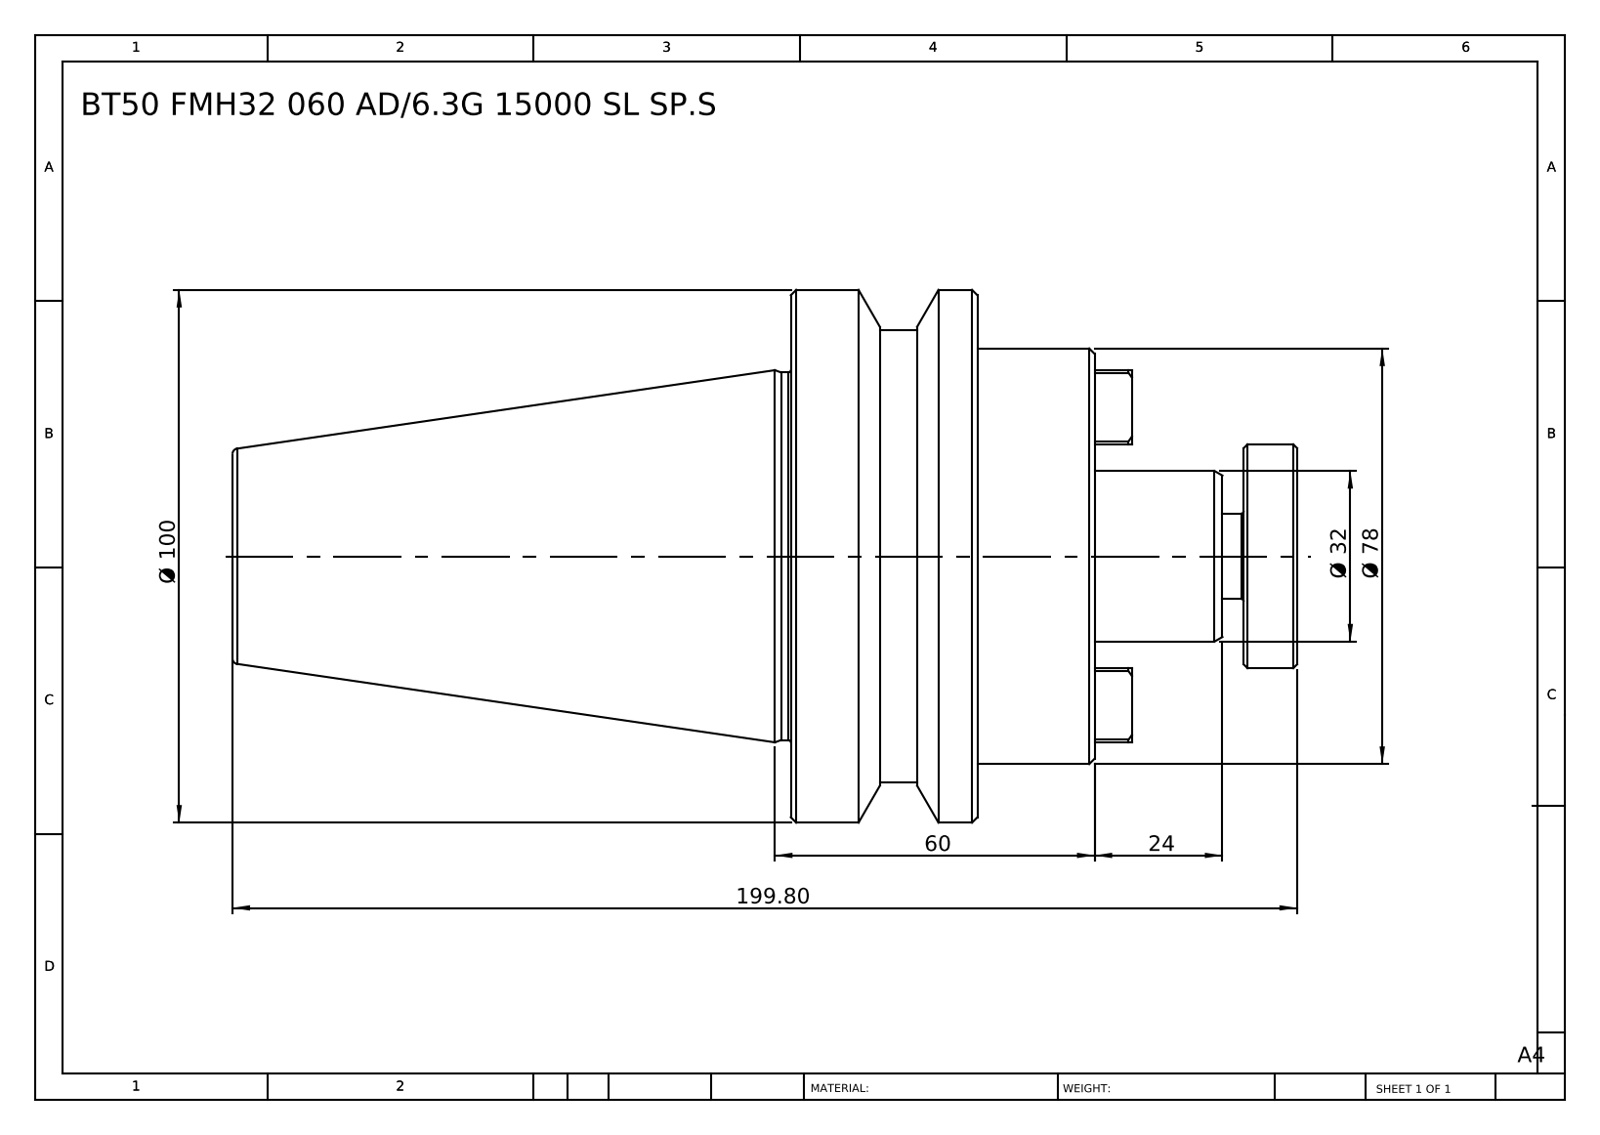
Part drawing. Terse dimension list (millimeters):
name: BT50 FMH32 060 AD-6.3G 15000 SL SP.S
written by: SolidWorks 2014 (CONFIG_CONTROL_DESIGN)
unit: mm
bodies: 1 solid, 77 faces (35 planar, 16 cylindrical, 26 other)
size: 199.8 × 100 × 100
volume: 651 665 mm³; area: 56 488 mm²
bosses: 1× ⌀100, 1× ⌀85, 1× ⌀78, 1× ⌀69, 1× ⌀42, 1× ⌀32, 1× ⌀16
face distances: 57, 22, 35, 38, 60, 95, 199.8, 161.8, 139.8, 104.8
